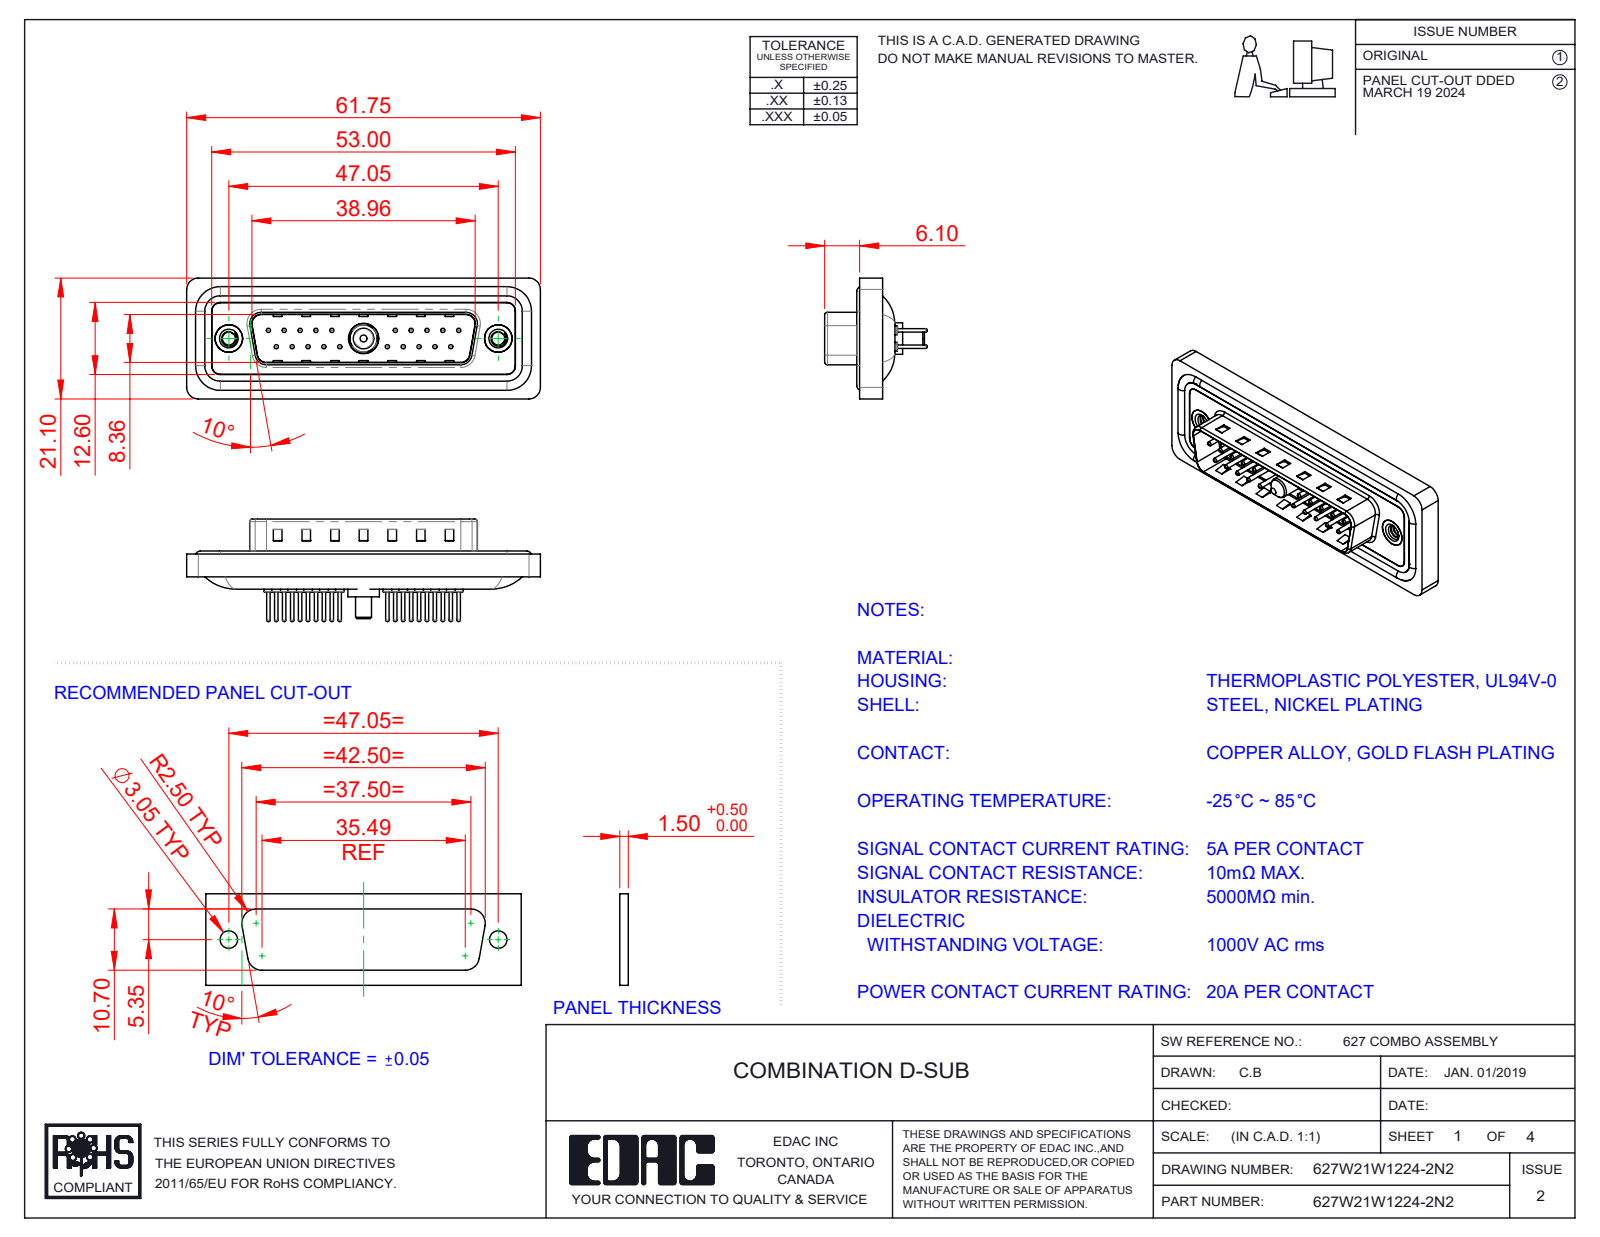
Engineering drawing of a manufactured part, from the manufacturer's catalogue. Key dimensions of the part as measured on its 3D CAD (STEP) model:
Part name (STEP PRODUCT): 627Combo Waterproof Housing_25 Contacts; 627Combo Threaded Rivet_2; Power Pin_20A S; 627Combo Shell Rear_25 Contacts (+5 more)
STEP written by: SolidWorks 2023 (CONFIG_CONTROL_DESIGN)
Units: millimetres
Bodies: 29 solids, 1262 faces (359 planar, 487 cylindrical, 416 other)
Overall size (bounding box): 61.75 × 21.1 × 17.9
Volume: 7 198 mm³ · Surface area: 11 953 mm²
Round holes (diameter × count): ⌀0.75 ×20, ⌀1.6 ×20, ⌀2 ×20, ⌀2.26 ×2, ⌀4 ×2, ⌀4.8 ×2, ⌀5 ×2, ⌀4.85 ×1, ⌀5.3 ×1
Round bosses / shafts (diameter × count): ⌀1.5 ×20, ⌀0.6 ×20, ⌀1.6 ×4, ⌀4.9 ×2, ⌀5.5 ×1, ⌀5.2 ×1, ⌀4.75 ×1, ⌀3.75 ×1
Partial cylindrical surfaces — rounded edges, fillets, slot ends (radius × count): R1.5 ×22, R2 ×18, R0.5 ×8, R1.6 ×8, R0.25 ×4, R0.6 ×4, R0.65 ×4, R0.9 ×4
Main face-to-face distances: 0.4, 1.5, 1.1, 1.6, 0.5, 3.1, 2.9, 4.1, 0.82, 9.58
Hole centre spacings: 3.16, 2.77, 5.54, 8.31, 5.04, 19.39, 20.97, 22.16
